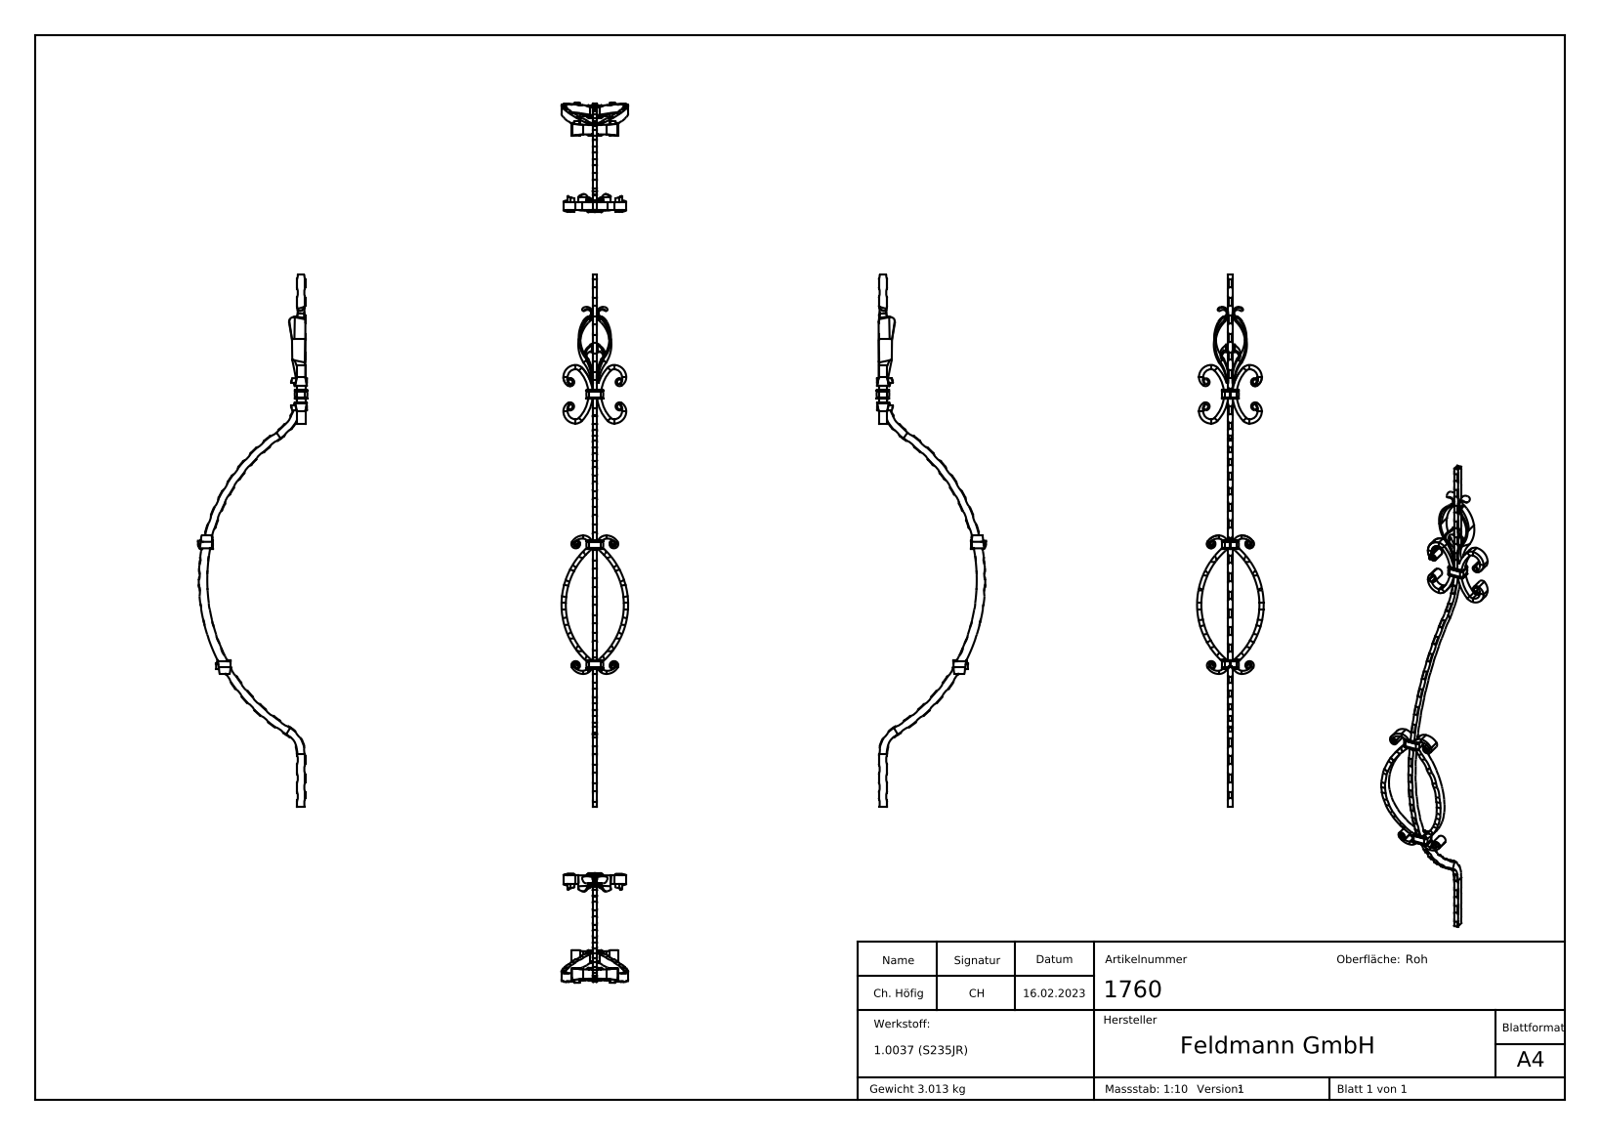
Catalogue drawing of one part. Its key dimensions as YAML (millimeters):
part_name: "1760"
step_written_by: "SolidWorks 2018 (CONFIG_CONTROL_DESIGN)"
units: millimeters
bodies: {solids: 29, faces: 1407, planar: 514, cylindrical: 420, other: 473}
overall_size: [1000, 207.3, 135]
volume: 386079
surface_area: 191428
partial_cylinders:
  - {radius: 0.7, count: 72}
  - {radius: 26, count: 67}
  - {radius: 36.54, count: 17}
  - {radius: 1, count: 12}
  - {radius: 5, count: 12}
  - {radius: 14.83, count: 12}
  - {radius: 36.04, count: 9}
  - {radius: 44.99, count: 9}
face_to_face_distances: [8, 16, 33.02, 24, 16.33, 225, 30, 507.5, 282.5, 29.99]
